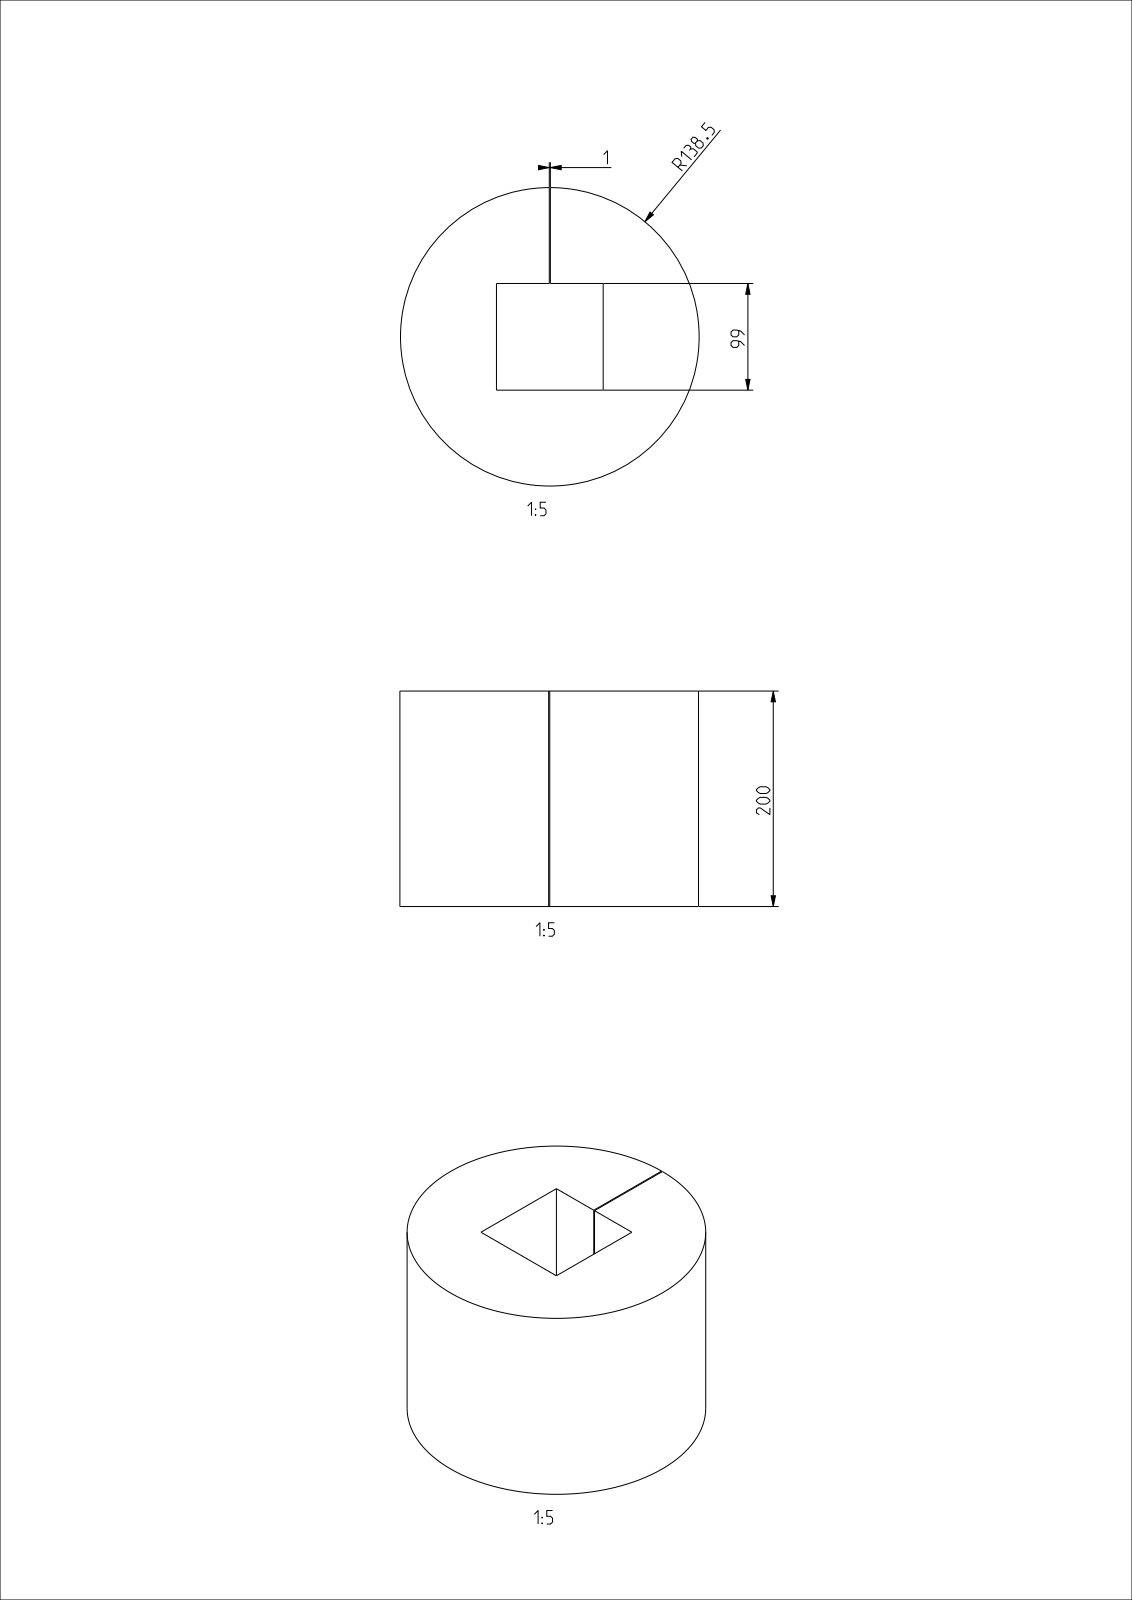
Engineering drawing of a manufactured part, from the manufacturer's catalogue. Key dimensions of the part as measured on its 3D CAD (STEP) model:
Part name (STEP PRODUCT): 47675-M
STEP written by: CREO PARAMETRIC BY PTC INC, 2022281 (AUTOMOTIVE_DESIGN)
Units: millimetres
Bodies: 1 solid, 10 faces (9 planar, 1 cylindrical, 0 other)
Overall size (bounding box): 277 × 277 × 200
Volume: 10 070 000 mm³ · Surface area: 389 190 mm²
Round bosses / shafts (diameter × count): ⌀277 ×1
Main face-to-face distances: 200, 99, 49, 50, 1
